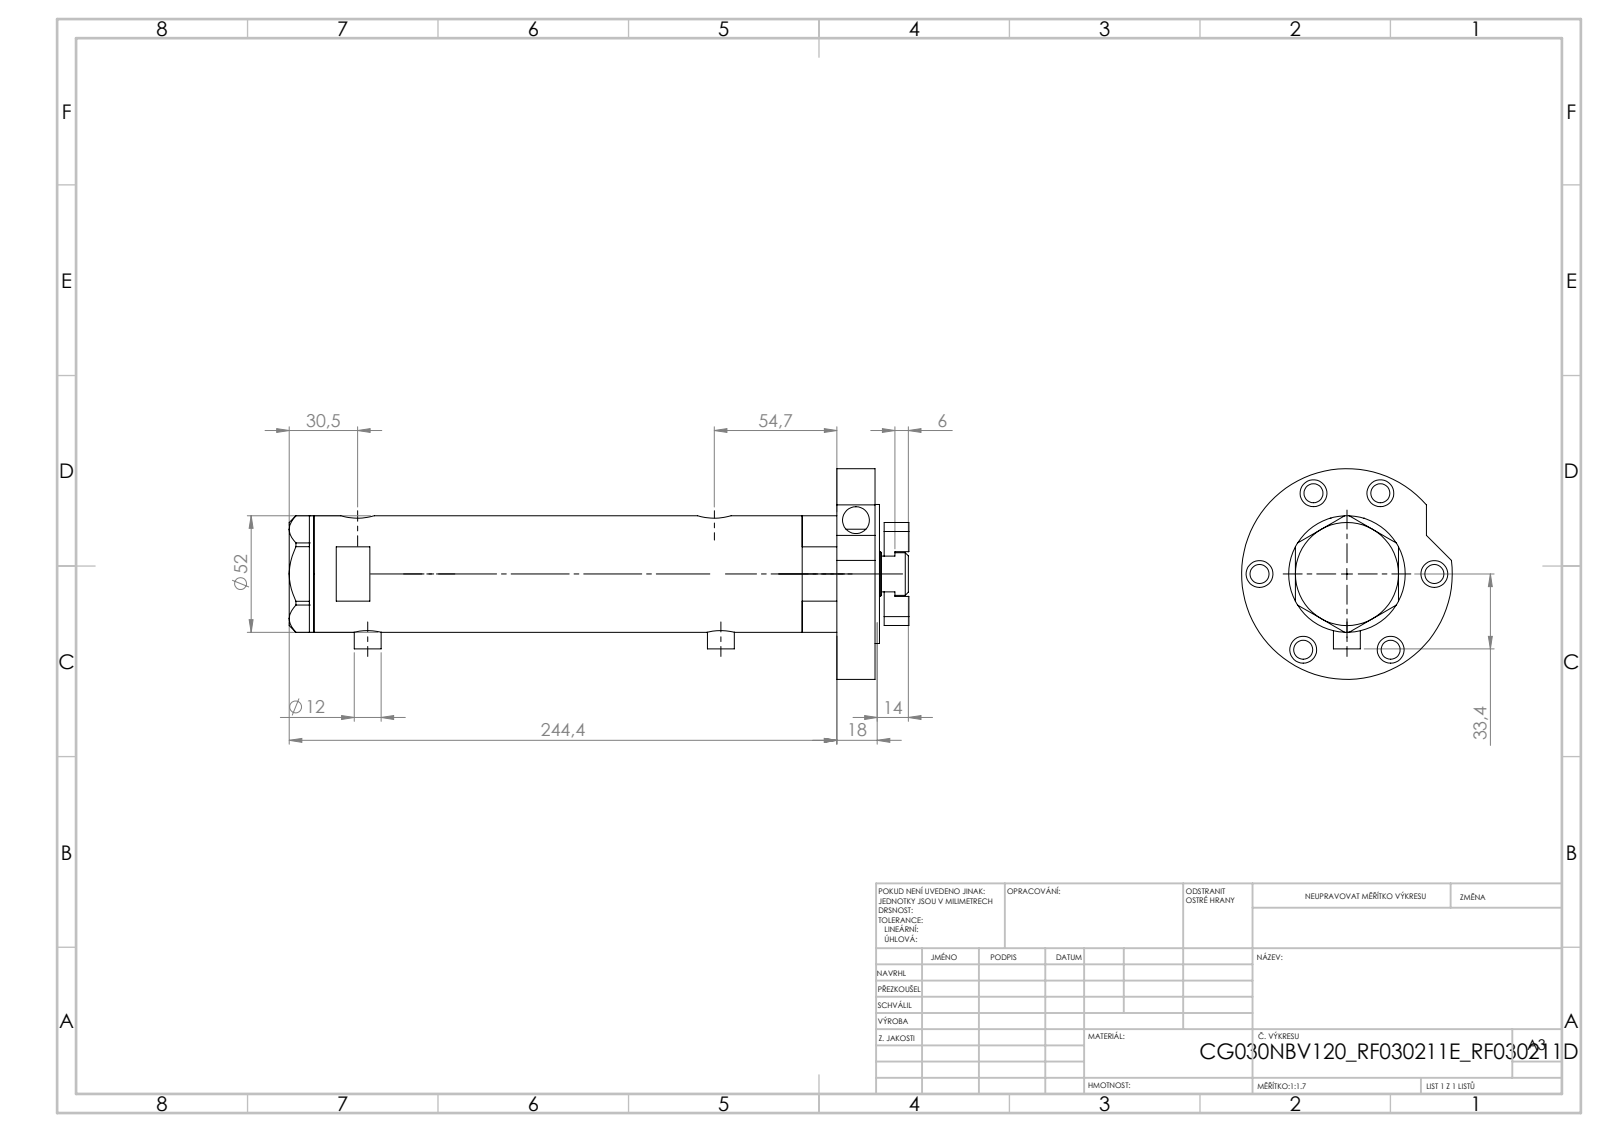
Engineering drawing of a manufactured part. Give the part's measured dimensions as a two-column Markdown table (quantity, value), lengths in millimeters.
| quantity | value |
| --- | --- |
| part name | V270CG_VC; V270CG_MIDDLE; V270CG_RF211E; V270CG_RF211D (+2 more) |
| STEP written by | SolidWorks 2019 (CONFIG_CONTROL_DESIGN) |
| units | millimeters |
| bodies | 7 solids, 218 faces (100 planar, 98 cylindrical, 20 other) |
| overall size | 276.5 × 94 × 94 |
| volume | 578 143 mm³ |
| surface area | 133 354 mm² |
| round holes (diameter × count) | 12 × 7, 8.5 × 6, 5.1 × 4, 9 × 4, 9.73 × 2, 12.5 × 2, 15 × 2, 6.5 × 1, 20 × 1, 21.5 × 1, 30 × 1, 33 × 1 |
| round bosses / shafts (diameter × count) | 12 × 2, 94 × 1, 62 × 1, 52 × 1, 38 × 1, 19 × 1 |
| main face-to-face distances | 17, 233.4, 250.4, 2, 252.4, 11, 181.5, 51.9, 68.9, 70.9 |
| hole center spacings | 39, 16.74, 37.57, 46.81, 10, 22.37, 22.95, 28.26 |
